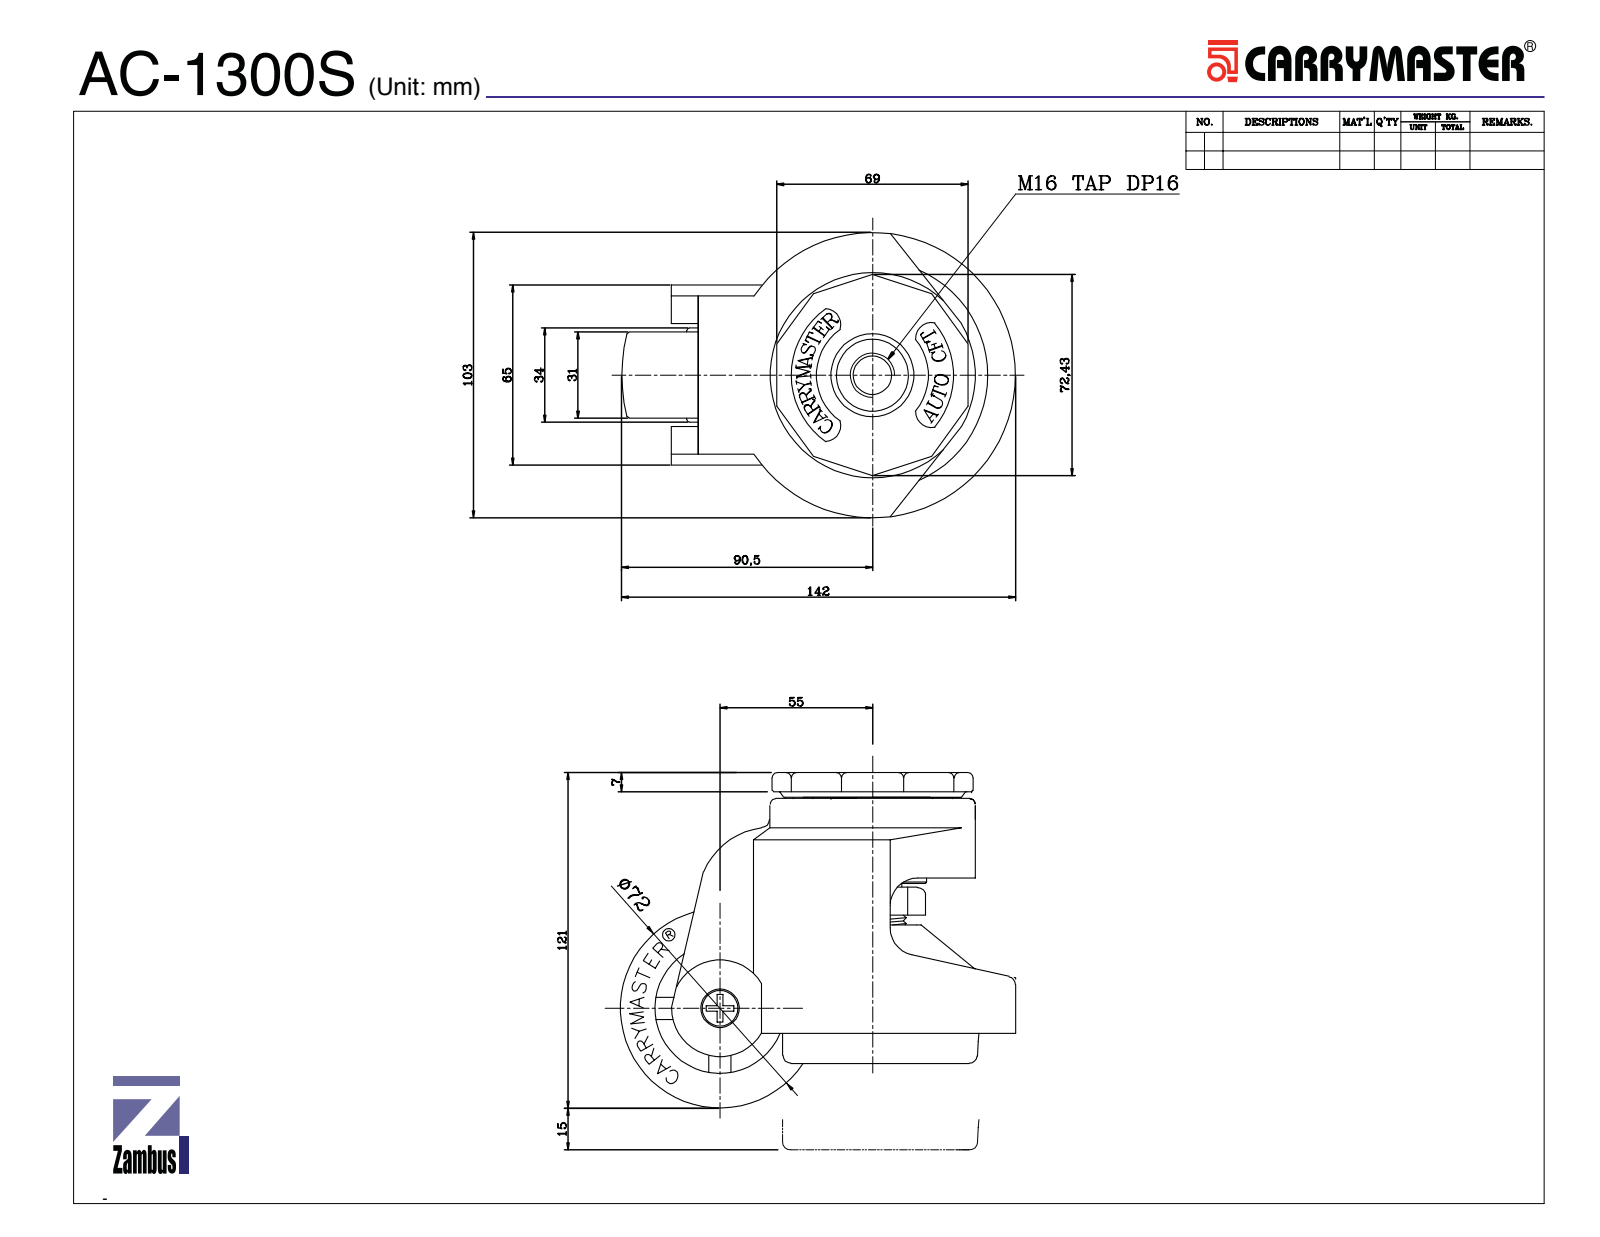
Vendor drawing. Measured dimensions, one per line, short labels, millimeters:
name: AC-1300S
written by: SolidWorks 2015 (CONFIG_CONTROL_DESIGN)
unit: mm
bodies: 43 solids, 2559 faces (1896 planar, 266 cylindrical, 397 other)
size: 142.5 × 120.5 × 104.4
volume: 579 063 mm³; area: 140 906 mm²
holes: 2× ⌀6.8, 1× ⌀1.63, 1× ⌀9.7, 1× ⌀12.2, 1× ⌀13, 1× ⌀14, 1× ⌀17.5, 1× ⌀22, 1× ⌀30, 1× ⌀41.4, 1× ⌀47, 1× ⌀83
bosses: 2× ⌀16, 1× ⌀103, 1× ⌀74, 1× ⌀41.2, 1× ⌀40, 1× ⌀39, 1× ⌀35, 1× ⌀25.4
rounds: 30× R0.5, 20× R5, 8× R8, 6× R3, 4× R2, 4× R4.5, 2× R10, 1× R1.49
face distances: 35.5, 50, 8, 24.5, 2.5, 37.5, 56, 12.5, 33.5, 43.5
hole spacings: 26.29
